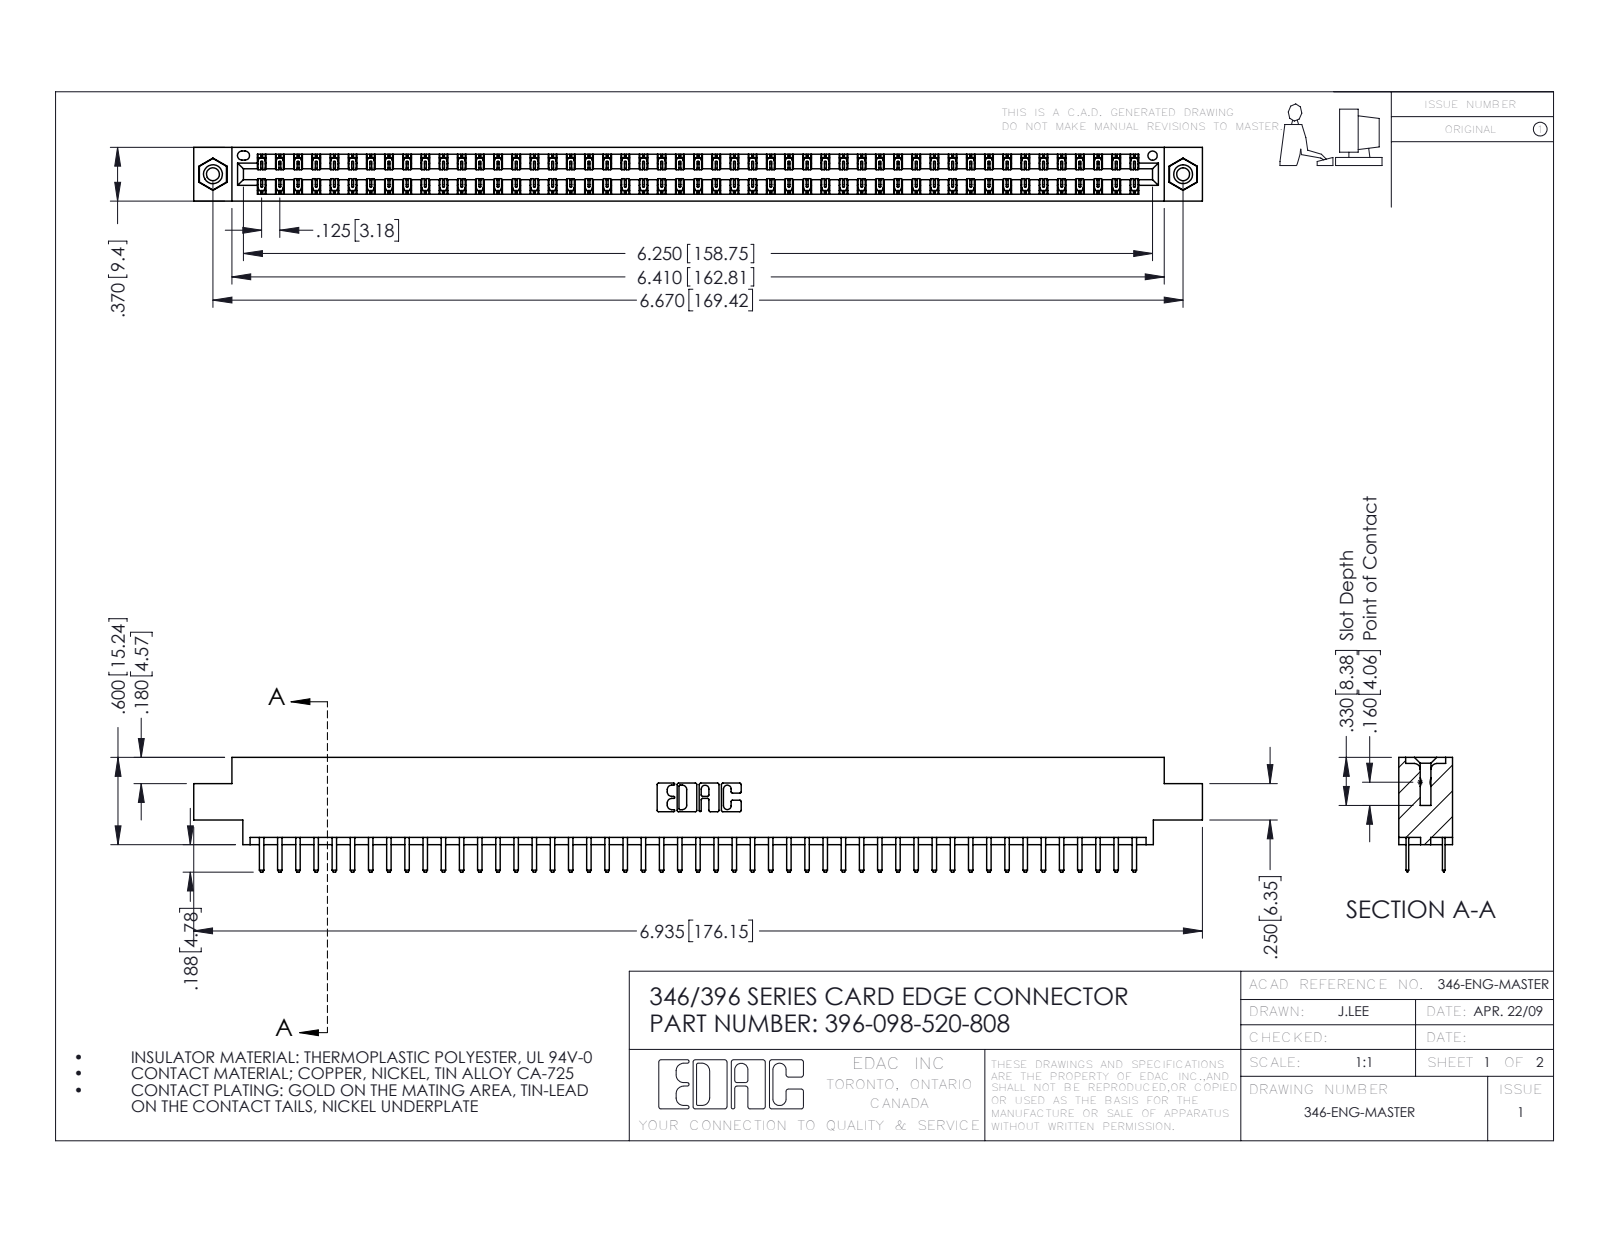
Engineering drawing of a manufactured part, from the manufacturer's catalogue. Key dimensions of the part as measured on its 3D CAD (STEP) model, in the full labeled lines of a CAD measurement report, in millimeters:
Part name (STEP PRODUCT): 396-098-520-808; 345-250-001_345-250-003-102; 346 Part_0.170 Offset - 0.156 Dia-TI; 345-292-001_345-293-120
STEP written by: SolidWorks 2016 (CONFIG_CONTROL_DESIGN)
Units: millimetres
Bodies: 101 solids, 5674 faces (3738 planar, 1920 cylindrical, 16 other)
Overall size (bounding box): 176.1 × 20 × 9.4
Volume: 17 030 mm³ · Surface area: 23 610 mm²
Round holes (diameter × count): ⌀2.3 ×2, ⌀3.2 ×2, ⌀4 ×2, ⌀1.6 ×1
Round bosses / shafts (diameter × count): ⌀3.9 ×2
Partial cylindrical surfaces — rounded edges, fillets, slot ends (radius × count): R0.2 ×147, R0.3 ×102, R0.3 ×22, R0.2 ×6, R0.8 ×6, R0.7 ×3, R0.4 ×2, R0.6 ×2
Main face-to-face distances: 1.2, 8.2, 6.4, 9.4, 7, 1.8, 7.6, 0.6, 5.6, 3.8
Hole centre spacings: 6.2, 164.1, 169.4
